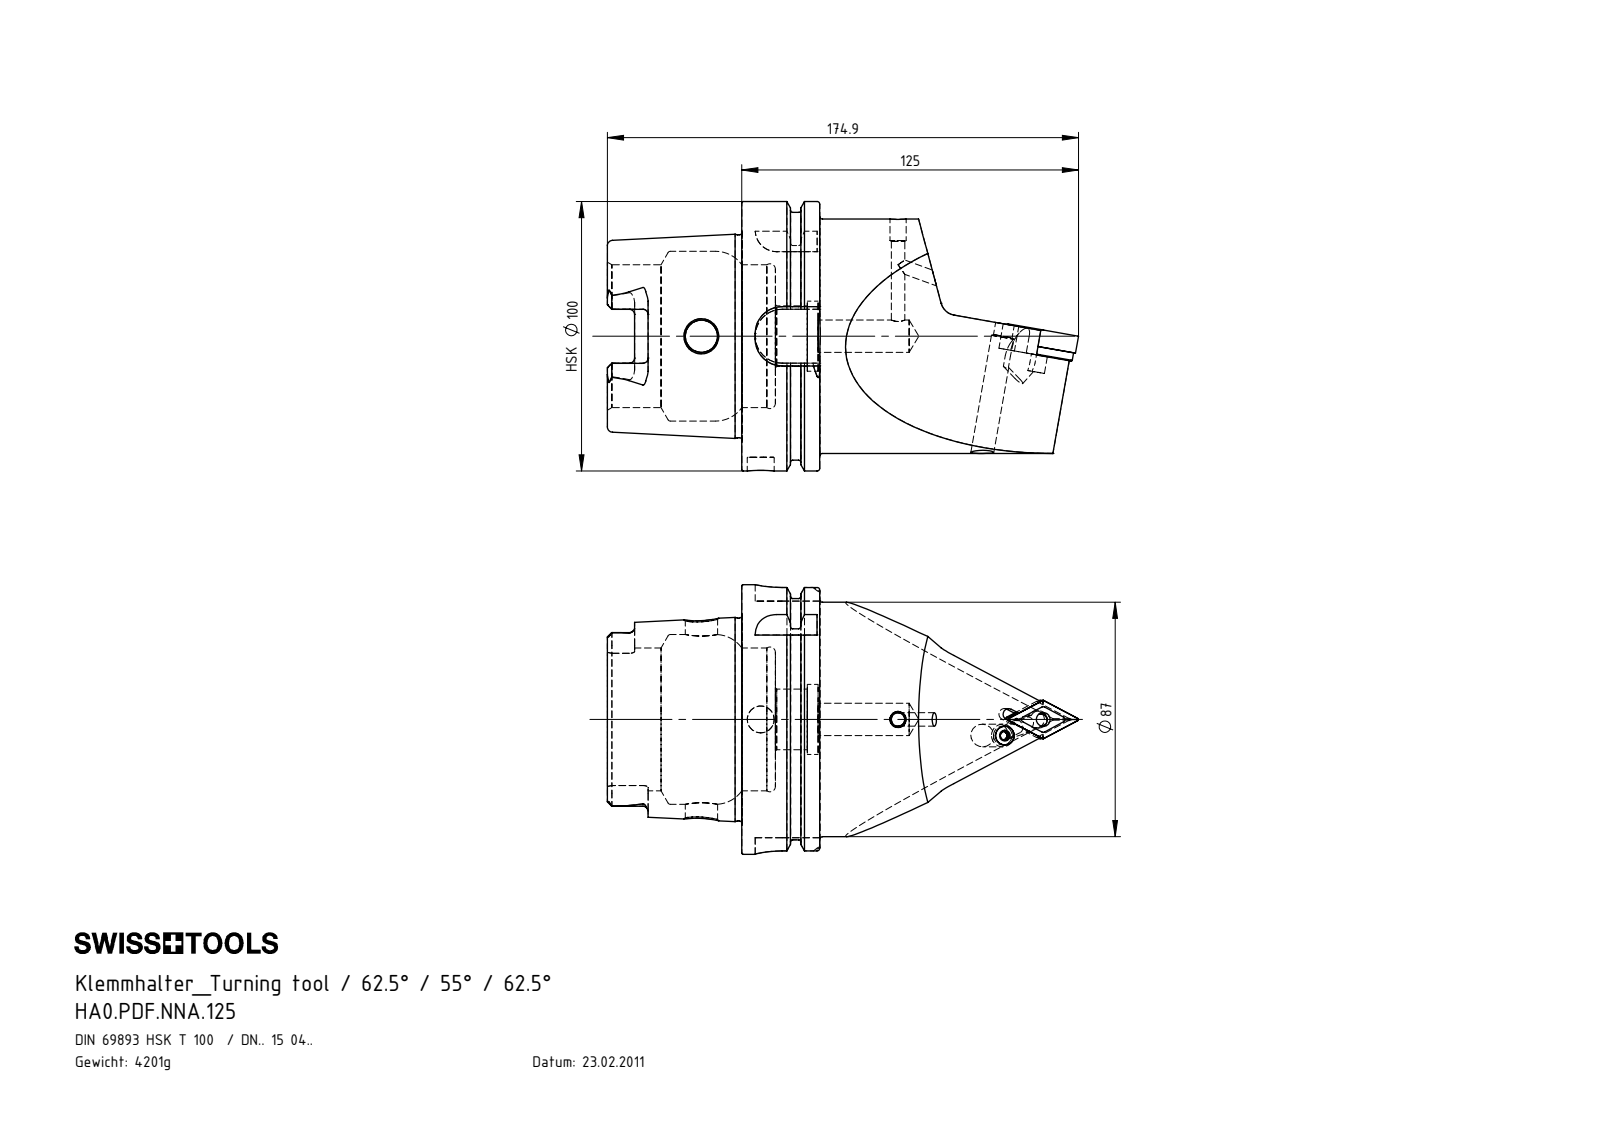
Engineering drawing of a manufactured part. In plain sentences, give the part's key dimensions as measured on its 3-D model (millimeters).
The part is named "HA0-PDF.NNA.125; WDF-ER3.101.000_A; WCD-ER4.101.017_A; KVT_MB_600_060 (+3 more)". Its 3-D file was written by "SolidWorks 2012 (CONFIG_CONTROL_DESIGN)". It is 7 solids with 356 faces: 111 planar, 97 cylindrical and 148 other. Overall it measures 174.9 by 100 by 100 millimeters. Its volume is 536 061 cubic millimeters and its surface area 70 570 square millimeters. Round holes: 2 of diameter 5, 2 of diameter 12, 1 of diameter 5.16, 1 of diameter 6.4, 1 of diameter 7, 1 of diameter 8.4, 1 of diameter 10, 1 of diameter 22.5, 1 of diameter 26, 1 of diameter 53, 1 of diameter 63. Round bosses or shafts: 1 of diameter 100, 1 of diameter 91.95, 1 of diameter 87, 1 of diameter 75.26, 1 of diameter 8, 1 of diameter 7.9, 1 of diameter 6.4, 1 of diameter 6. Partial cylindrical surfaces (rounded edges, fillets, slot ends): 6 of radius 1.9, 4 of radius 0.4, 4 of radius 1, 3 of radius 10, 2 of radius 2.5, 2 of radius 4.83, 2 of radius 4.88, 1 of radius 2.1. The main face-to-face distances are 12.45, 28.95, 16.5, 49.9, 62.35, 78.85, 87.8, 78.2, 28.3, 15.85. The hole center spacings are 15.6, 51.
